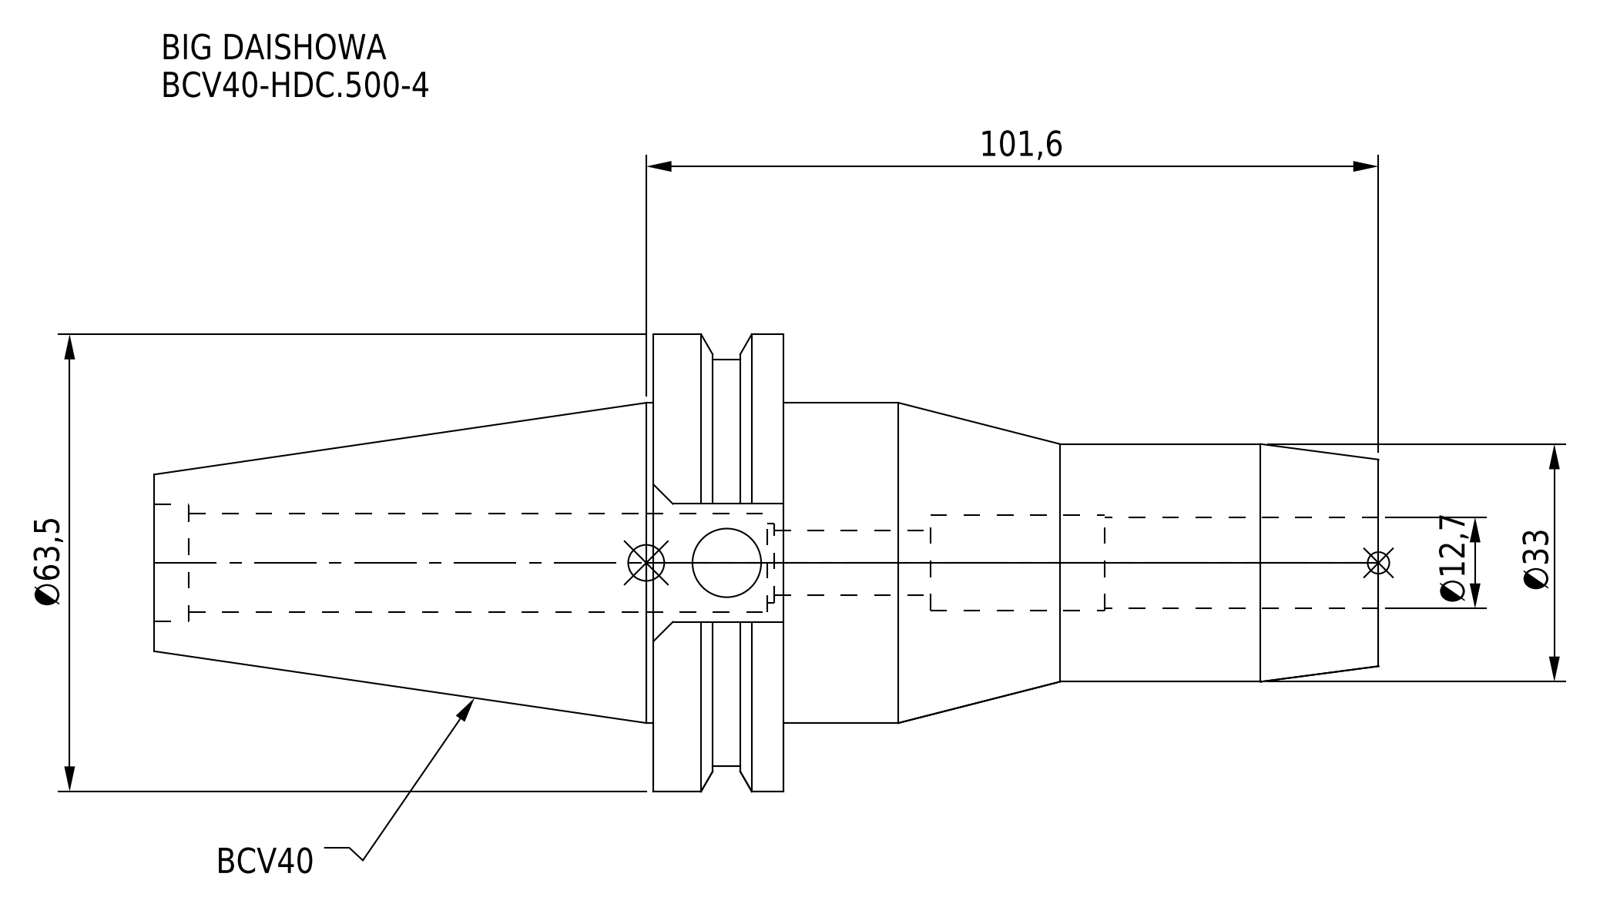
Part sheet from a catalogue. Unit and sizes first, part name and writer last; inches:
Units: inches
Overall size (bounding box): 6.687 × 2.5 × 2.415
Round holes (diameter × count): ⌀0.354 ×1, ⌀0.375 ×1, ⌀0.433 ×1, ⌀0.5 ×1, ⌀0.52 ×1, ⌀0.535 ×1, ⌀0.643 ×1
Round bosses / shafts (diameter × count): ⌀2.5 ×1, ⌀2.219 ×1, ⌀1.75 ×1, ⌀1.299 ×1
Main face-to-face distances: 0.711, 3.25, 3.961, 6.687, 3.437, 2.726, 1.872, 0.645, 3.486, 0.236
Volume: 11.1 in³ · Surface area: 50.11 in²
Bodies: 1 solid, 62 faces (24 planar, 28 cylindrical, 10 other)
Part name (STEP PRODUCT): BCV40-HDC_500-4
STEP written by: CREO PARAMETRIC BY PTC INC, 2016380 (AUTOMOTIVE_DESIGN)
